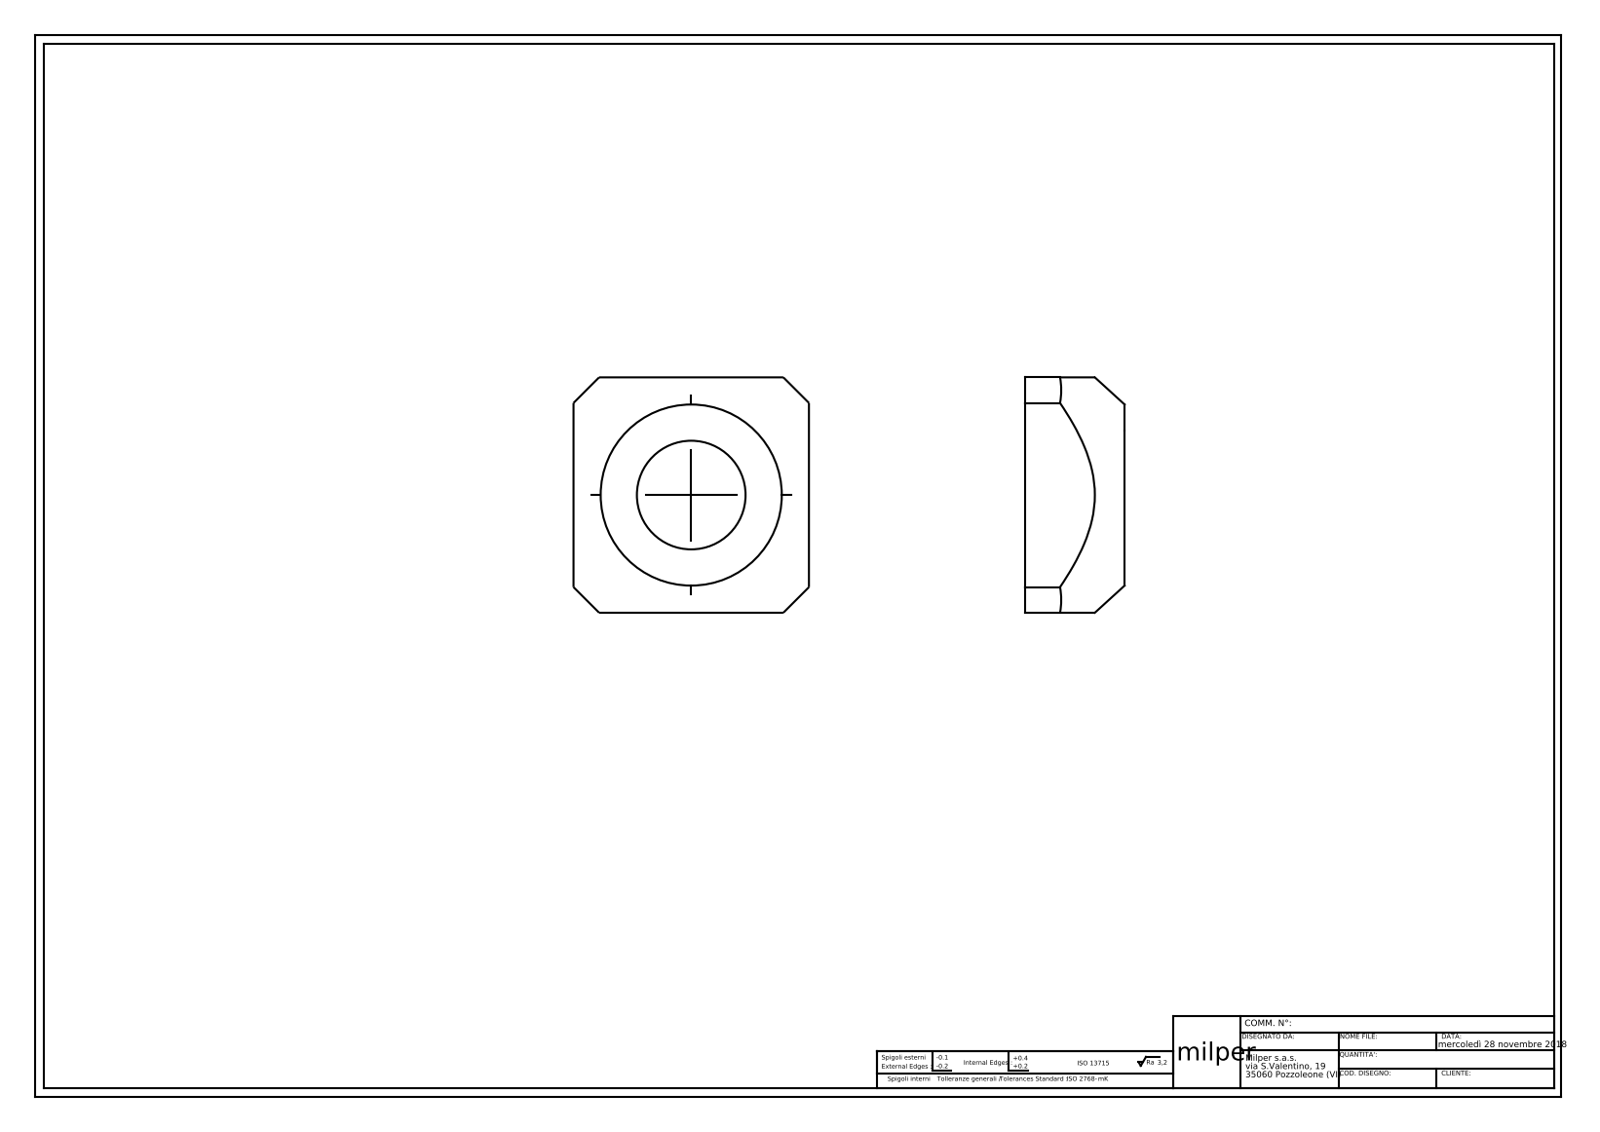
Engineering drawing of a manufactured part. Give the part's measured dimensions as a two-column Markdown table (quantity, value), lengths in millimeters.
| quantity | value |
| --- | --- |
| part name | dado-M6-3D |
| STEP written by | SolidWorks 2018 (CONFIG_CONTROL_DESIGN) |
| units | millimeters |
| bodies | 1 solid, 14 faces (10 planar, 2 cylindrical, 2 other) |
| overall size | 13 × 13 × 5.5 |
| volume | 629 mm³ |
| surface area | 564 mm² |
| round holes (diameter × count) | 6 × 1 |
| main face-to-face distances | 13, 5.5, 16.38 |
